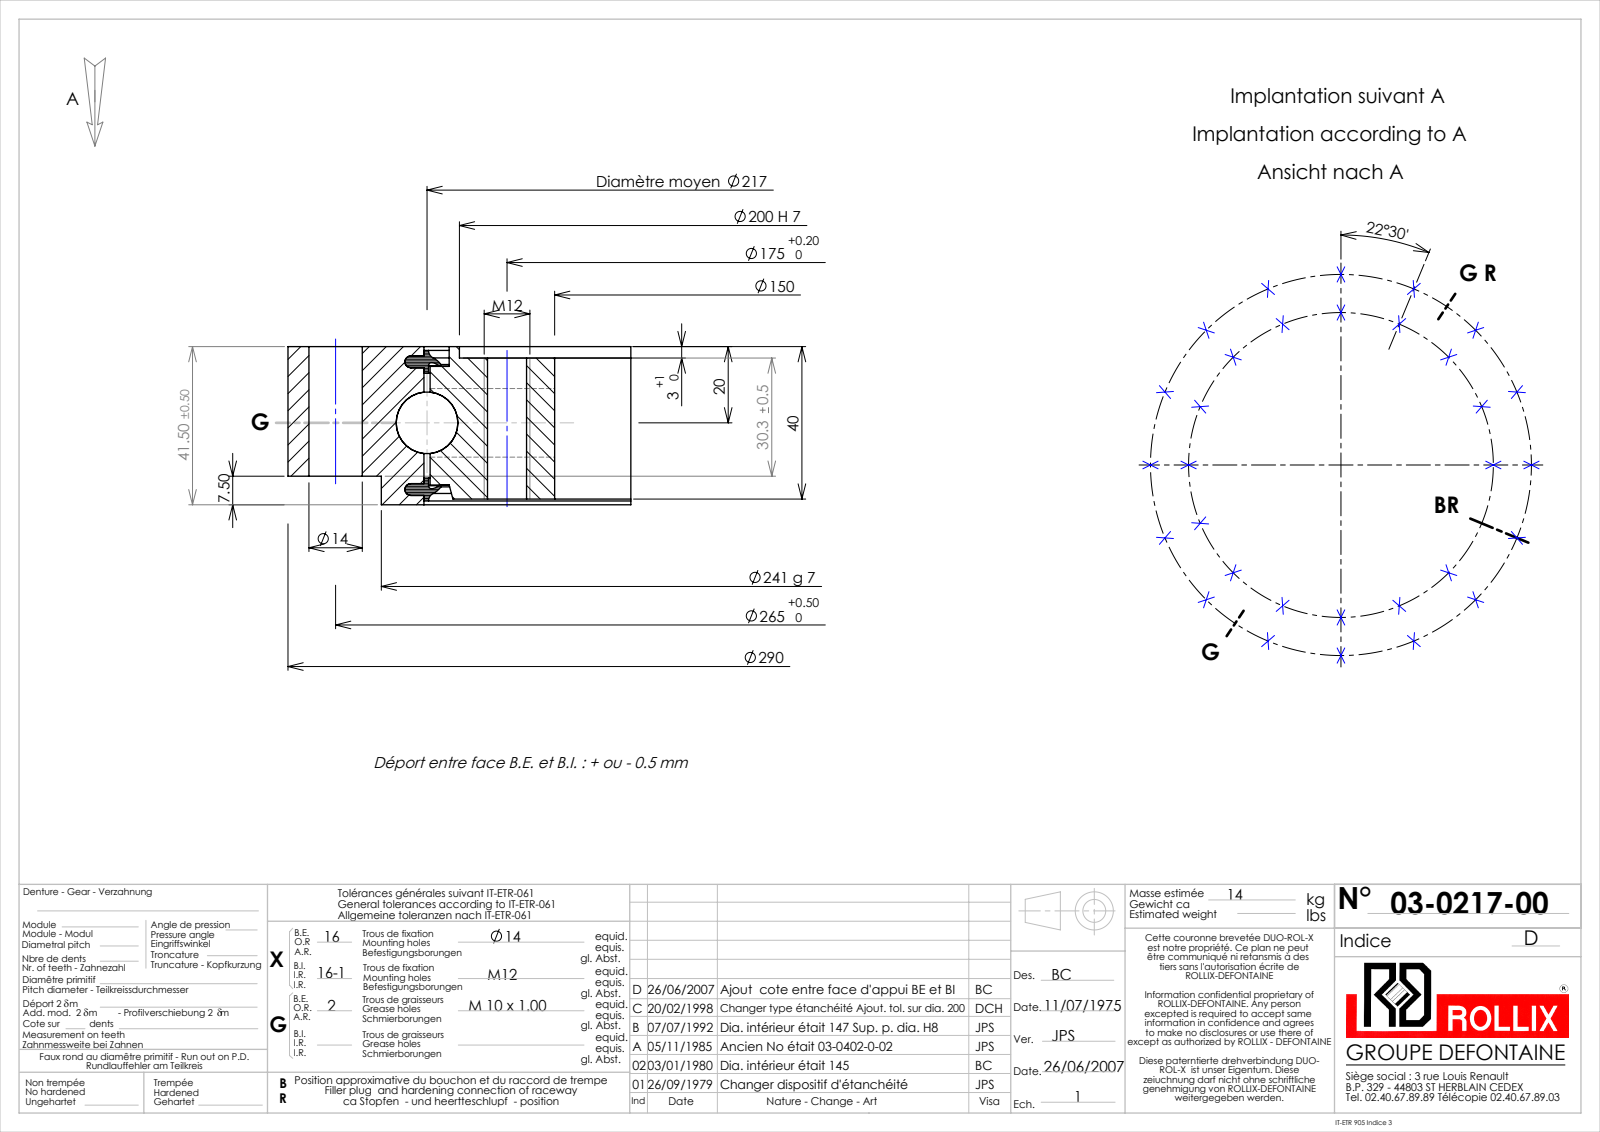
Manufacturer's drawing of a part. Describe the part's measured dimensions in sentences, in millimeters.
The part is named "03-0217-00". Its 3-D file was written by "SolidWorks 2016 (CONFIG_CONTROL_DESIGN)". It is 5 solids with 166 faces: 20 planar, 100 cylindrical and 46 other. Overall it measures 290 by 290 by 41.5 millimeters. Its volume is 1 473 000 cubic millimeters and its surface area 303 183 square millimeters. Round holes: 16 of diameter 14, 15 of diameter 10.25, 2 of diameter 9, 1 of diameter 150, 1 of diameter 200, 1 of diameter 216.22, 1 of diameter 218.62. Round bosses or shafts: 1 of diameter 290, 1 of diameter 241, 1 of diameter 215.38, 1 of diameter 205.38. The main face-to-face distances are 34, 6, 40, 37, 31, 3, 33.5, 5.55, 35.95, 2.45. The hole center spacings are 184.62, 203.98, 215.95, 61.56, 158.78, 87.5, 34.14, 45.
